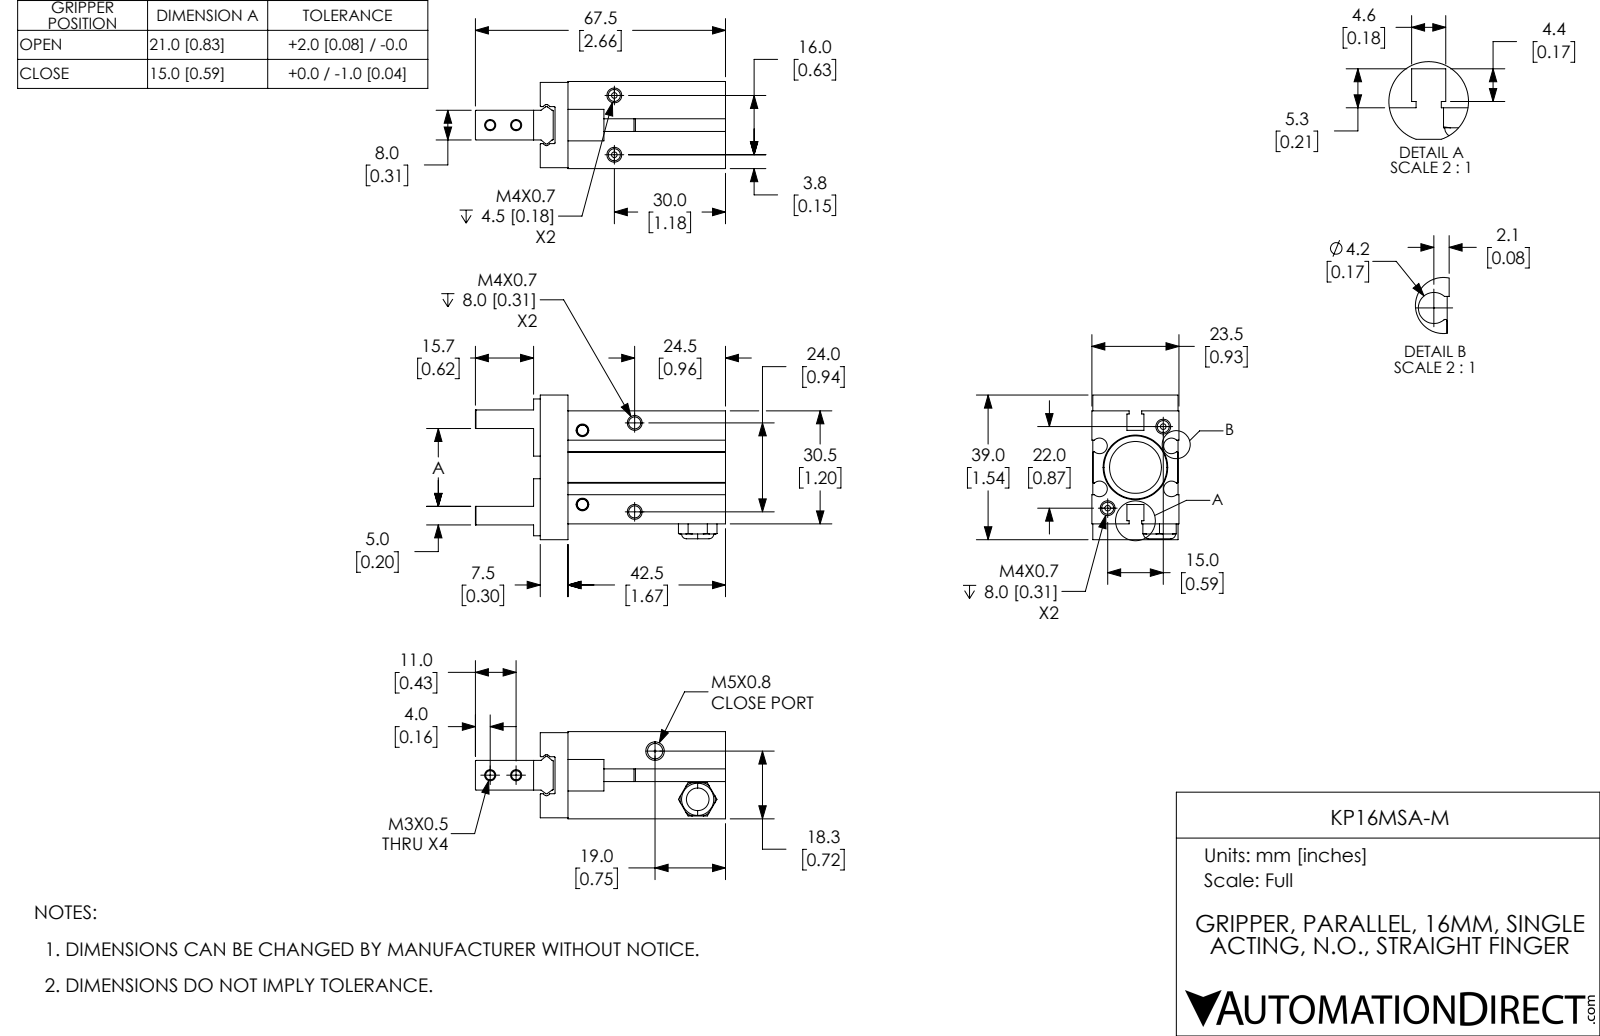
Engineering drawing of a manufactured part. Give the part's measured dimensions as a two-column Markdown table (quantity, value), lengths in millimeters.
| quantity | value |
| --- | --- |
| part name | KP16MSA-M-3; KP16MSA-M-2; KP16MSA-M-1; KP16MSA-M |
| STEP written by | SolidWorks 2017 (CONFIG_CONTROL_DESIGN) |
| units | millimeters |
| bodies | 3 solids, 263 faces (125 planar, 68 cylindrical, 70 other) |
| overall size | 67.5 × 39 × 23.5 |
| volume | 30 422 mm³ |
| surface area | 13 537 mm² |
| round holes (diameter × count) | 3.24 × 6, 0.5 × 2, 2.46 × 2, 4.02 × 2, 4.13 × 2, 6.1 × 1, 14 × 1, 17 × 1 |
| partial cylindrical surfaces (radius × count) | 0.2 × 10, 2.1 × 4, 0.4 × 2, 0.5 × 2, 1 × 2 |
| main face-to-face distances | 7.5, 15.75, 4, 30.5, 23.2, 15.7, 23.5, 7.2, 3.5, 16 |
| hole center spacings | 13.31, 27.68, 34.44, 7, 11.1, 16, 17.36, 18.2 |
